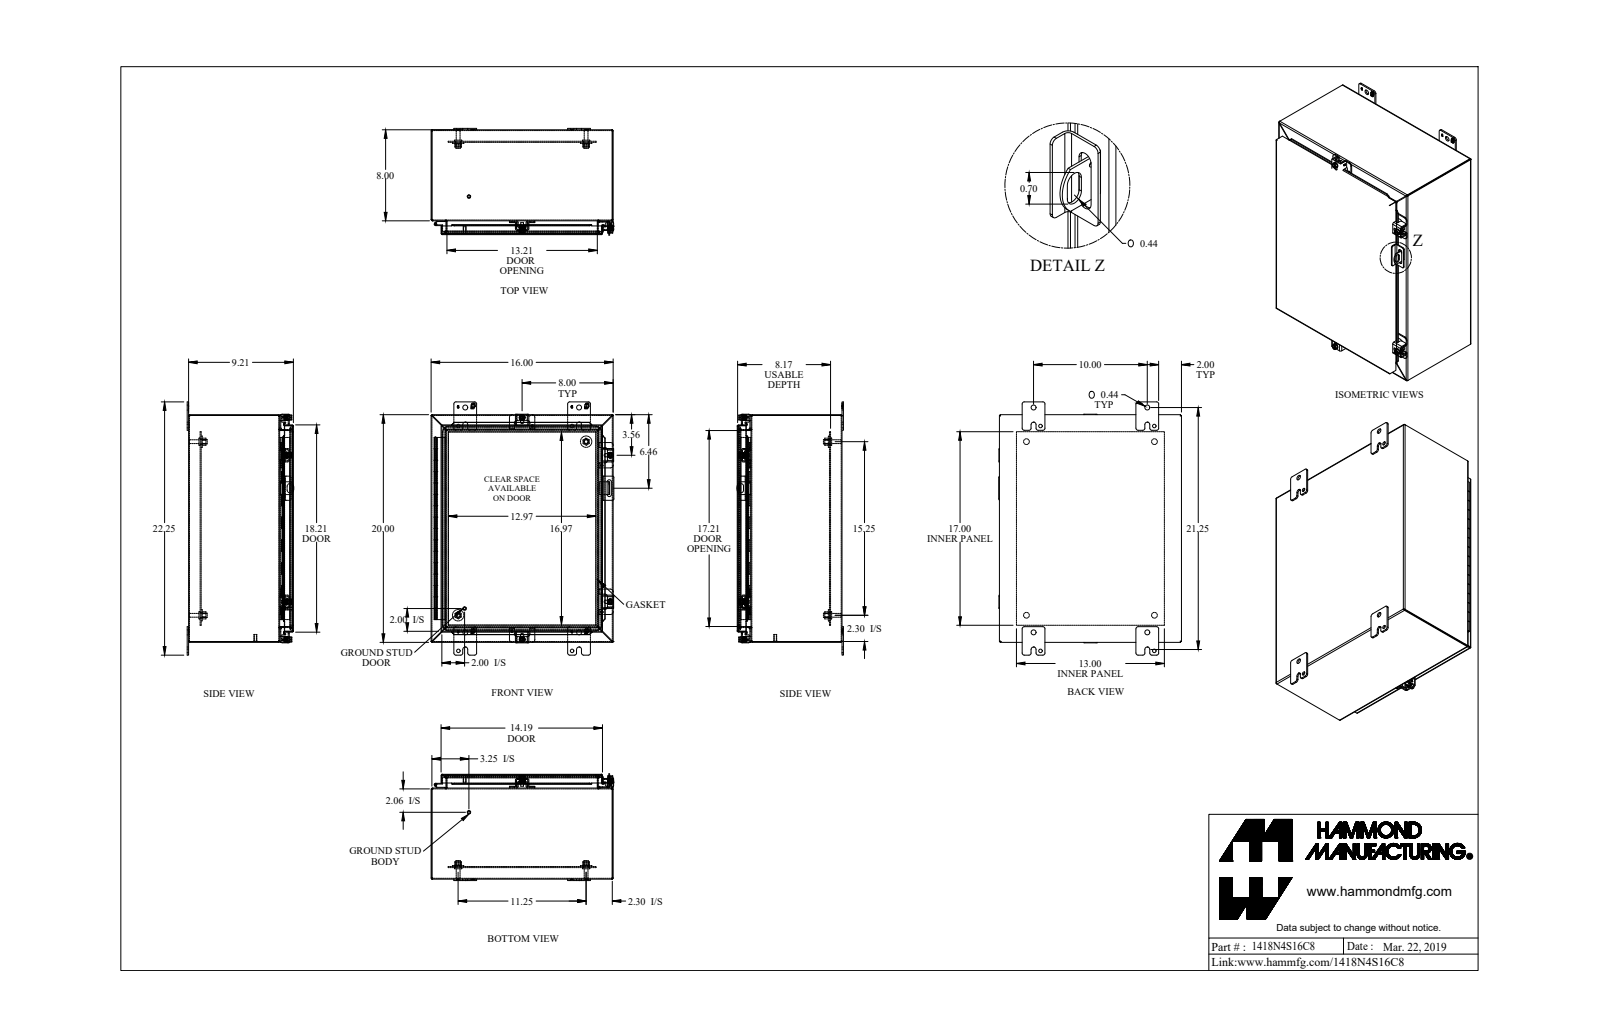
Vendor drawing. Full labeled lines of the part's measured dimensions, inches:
Part name (STEP PRODUCT): 1418N4S16C8_Default
STEP written by: SolidWorks 2019 (CONFIG_CONTROL_DESIGN)
Units: inches
Bodies: 39 solids, 1329 faces (728 planar, 467 cylindrical, 134 other)
Overall size (bounding box): 22.25 × 16.063 × 9.375
Volume: 131.8 in³ · Surface area: 3 504 in²
Round holes (diameter × count): ⌀0.213 ×4, ⌀0.265 ×4, ⌀0.313 ×4, ⌀0.375 ×4, ⌀0.437 ×4, ⌀0.5 ×4, ⌀0.307 ×2, ⌀0.445 ×2, ⌀0.11 ×1, ⌀0.125 ×1
Round bosses / shafts (diameter × count): ⌀0.65 ×4, ⌀0.5 ×4, ⌀0.39 ×4, ⌀0.375 ×4, ⌀0.332 ×4, ⌀0.244 ×4, ⌀1 ×2, ⌀0.313 ×2
Partial cylindrical surfaces — rounded edges, fillets, slot ends (radius × count): R0.188 ×26, R0.036 ×24, R0.108 ×24, R0.048 ×21, R0.143 ×21, R0.25 ×20, R0.125 ×10, R0.045 ×8
Main face-to-face distances: 0.072, 15.928, 9.066, 9.138, 0.072, 9.138, 0.937, 9.21, 19.928, 1.009
Hole centre spacings: 18.263, 6.013, 10, 2.434, 3.065, 11.041, 11.25, 15.25
